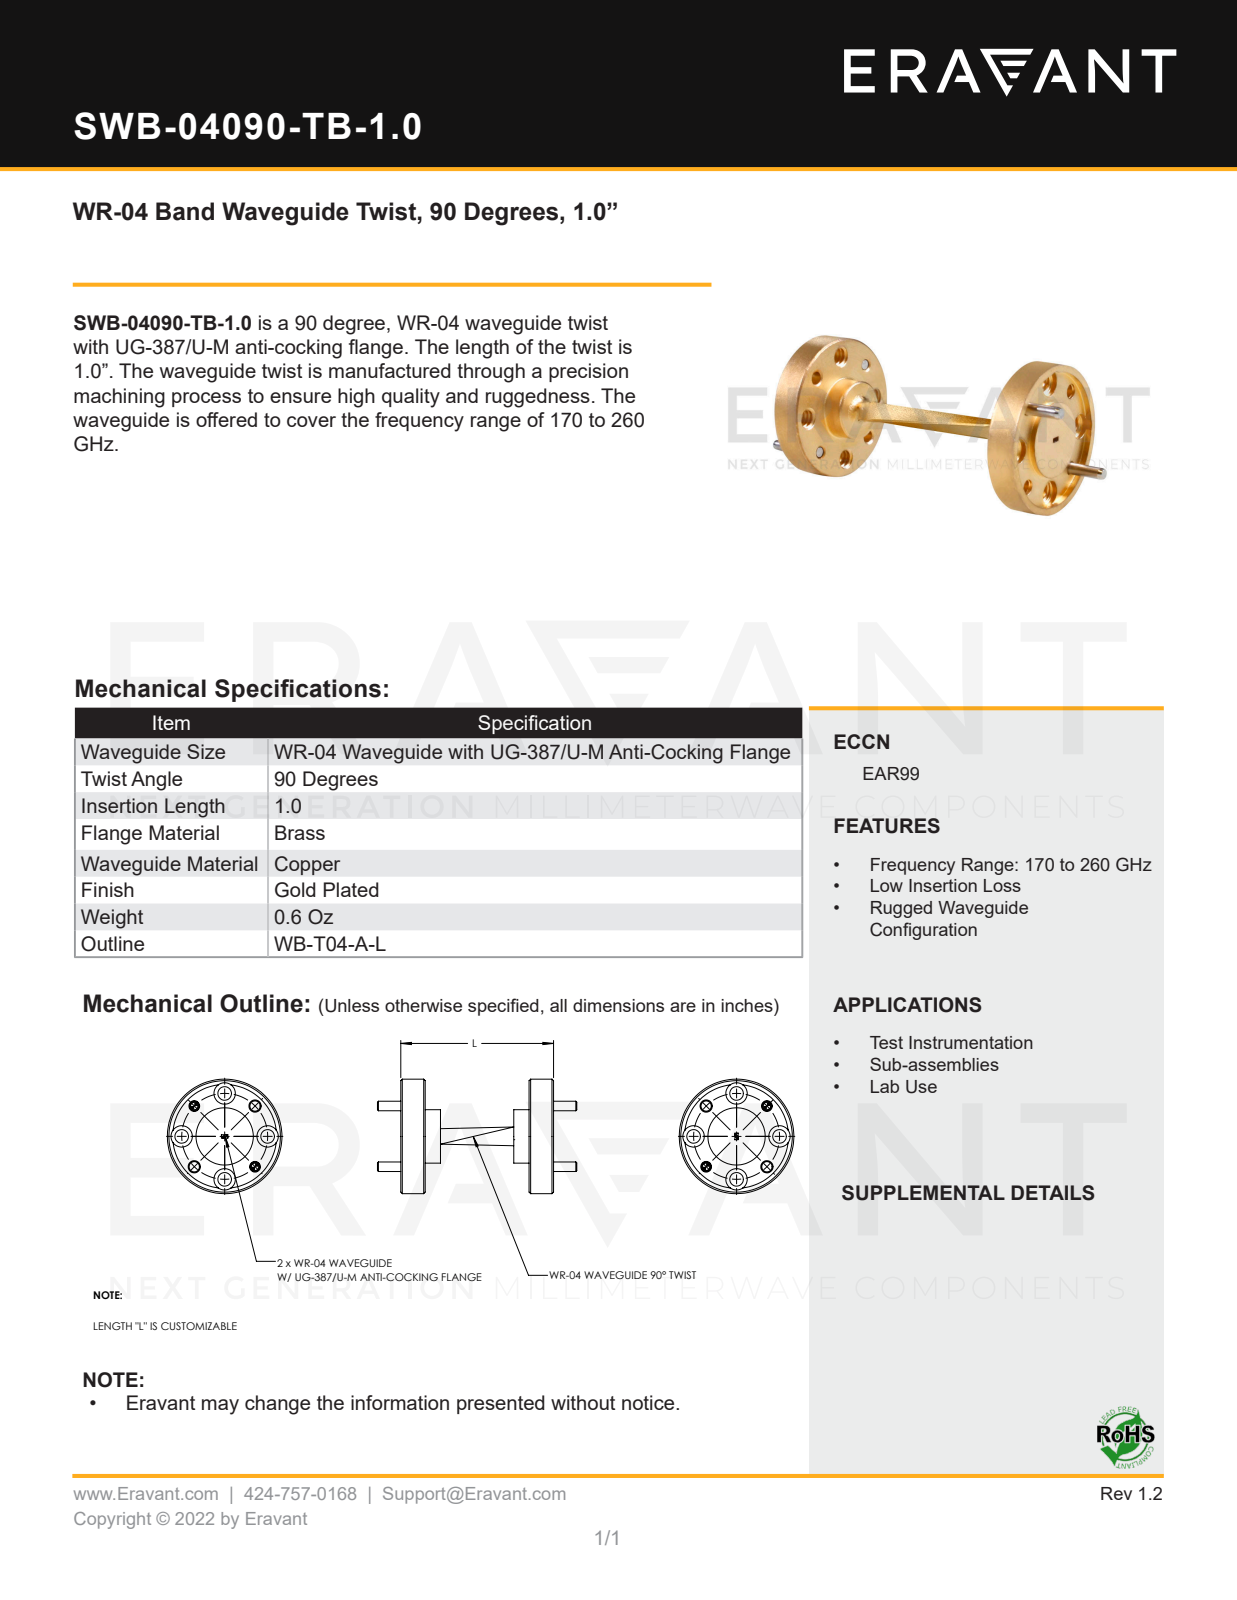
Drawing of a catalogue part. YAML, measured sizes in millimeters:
part_name: "SWB-04090-TB-1.0"
step_written_by: "SolidWorks 2021 (CONFIG_CONTROL_DESIGN)"
units: millimeters
bodies: {solids: 5, faces: 156, planar: 36, cylindrical: 76, other: 44}
overall_size: [33.1, 19.1, 19.1]
volume: 2360
surface_area: 2368
round_holes:
  - {diameter: 2.3, count: 4}
  - {diameter: 3.6, count: 4}
  - {diameter: 1.5, count: 2}
  - {diameter: 1.7, count: 2}
  - {diameter: 17.3, count: 1}
round_bosses_or_shafts:
  - {diameter: 1.6, count: 2}
  - {diameter: 19.1, count: 1}
  - {diameter: 9.5, count: 1}
  - {diameter: 8.9, count: 1}
face_to_face_distances: [17.3, 3.6, 20.8, 2.5, 24.4, 6.1, 18.3, 14.7, 24.9, 24.9]
hole_center_spacings: [5.5, 13.2, 10.1, 7.1, 7.1, 14.3, 10.1, 5.5]
